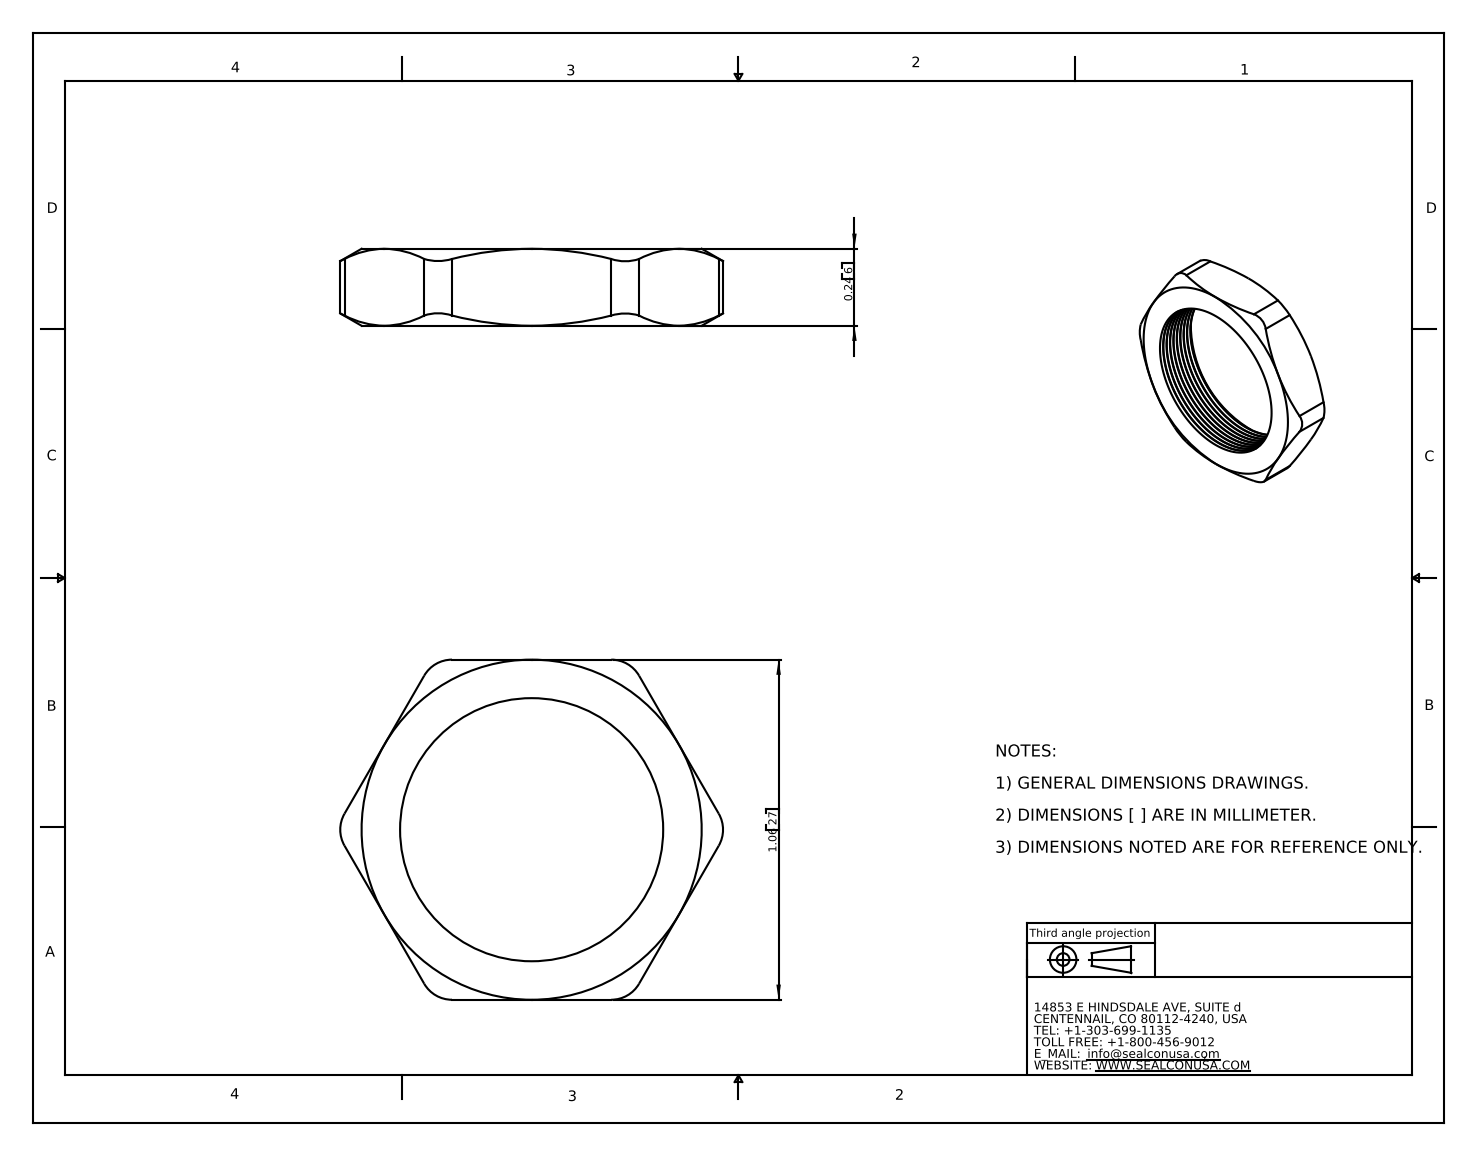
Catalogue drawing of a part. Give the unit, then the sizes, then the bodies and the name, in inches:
Units: inches
Overall size (bounding box): 1.193 × 1.06 × 0.24
Round holes (diameter × count): ⌀0.82 ×1
Partial cylindrical surfaces — rounded edges, fillets, slot ends (radius × count): R0.1 ×6
Main face-to-face distances: 1.06, 0.24
Volume: 0.098 in³ · Surface area: 2.85 in²
Bodies: 1 solid, 87 faces (8 planar, 25 cylindrical, 54 other)
Part name (STEP PRODUCT): NN-13
STEP written by: SolidWorks 2007 (CONFIG_CONTROL_DESIGN)
